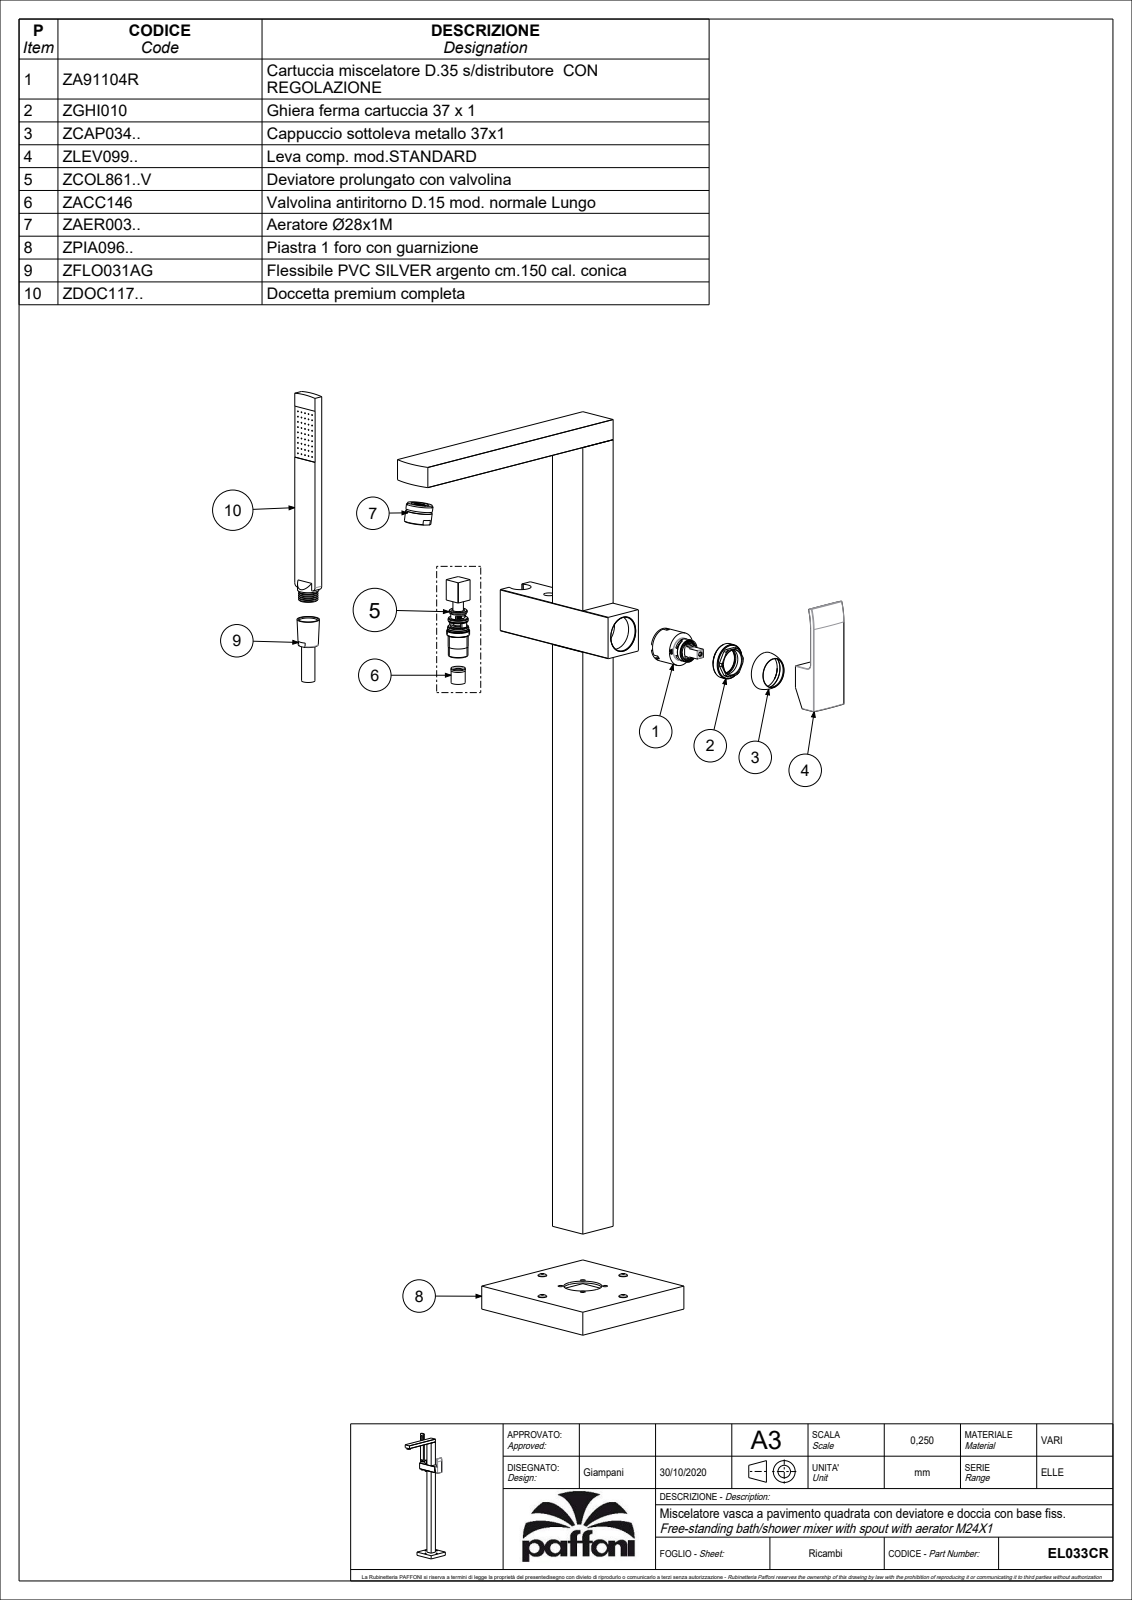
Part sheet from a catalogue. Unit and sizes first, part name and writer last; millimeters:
Units: millimetres
Overall size (bounding box): 927.5 × 330.5 × 198.6
Round holes (diameter × count): ⌀6 ×7, ⌀11 ×4, ⌀5 ×3, ⌀9 ×2, ⌀16 ×2, ⌀3 ×1, ⌀5.5 ×1, ⌀7.8 ×1, ⌀8 ×1, ⌀10 ×1, ⌀12.8 ×1, ⌀13 ×1
Round bosses / shafts (diameter × count): ⌀9 ×4, ⌀28 ×1, ⌀22.5 ×1, ⌀21.5 ×1, ⌀21 ×1, ⌀20.6 ×1, ⌀20.5 ×1, ⌀19 ×1
Partial cylindrical surfaces — rounded edges, fillets, slot ends (radius × count): R1.5 ×14, R0.5 ×10, R2 ×4, R4 ×2, R300 ×2, R9.75 ×1, R10.6 ×1, R13.25 ×1
Main face-to-face distances: 45, 25, 52.5, 97.5, 902, 877, 17.5, 27.5, 880, 855
Hole centre spacings: 7.5, 8.32, 8.6, 13.45, 15.13, 21.48, 21.93, 50.56
Volume: 2 869 000 mm³ · Surface area: 333 804 mm²
Bodies: 1 solid, 533 faces (217 planar, 182 cylindrical, 134 other)
Part name (STEP PRODUCT): EL033CR
STEP written by: CREO PARAMETRIC BY PTC INC, 2020044 (CONFIG_CONTROL_DESIGN)
